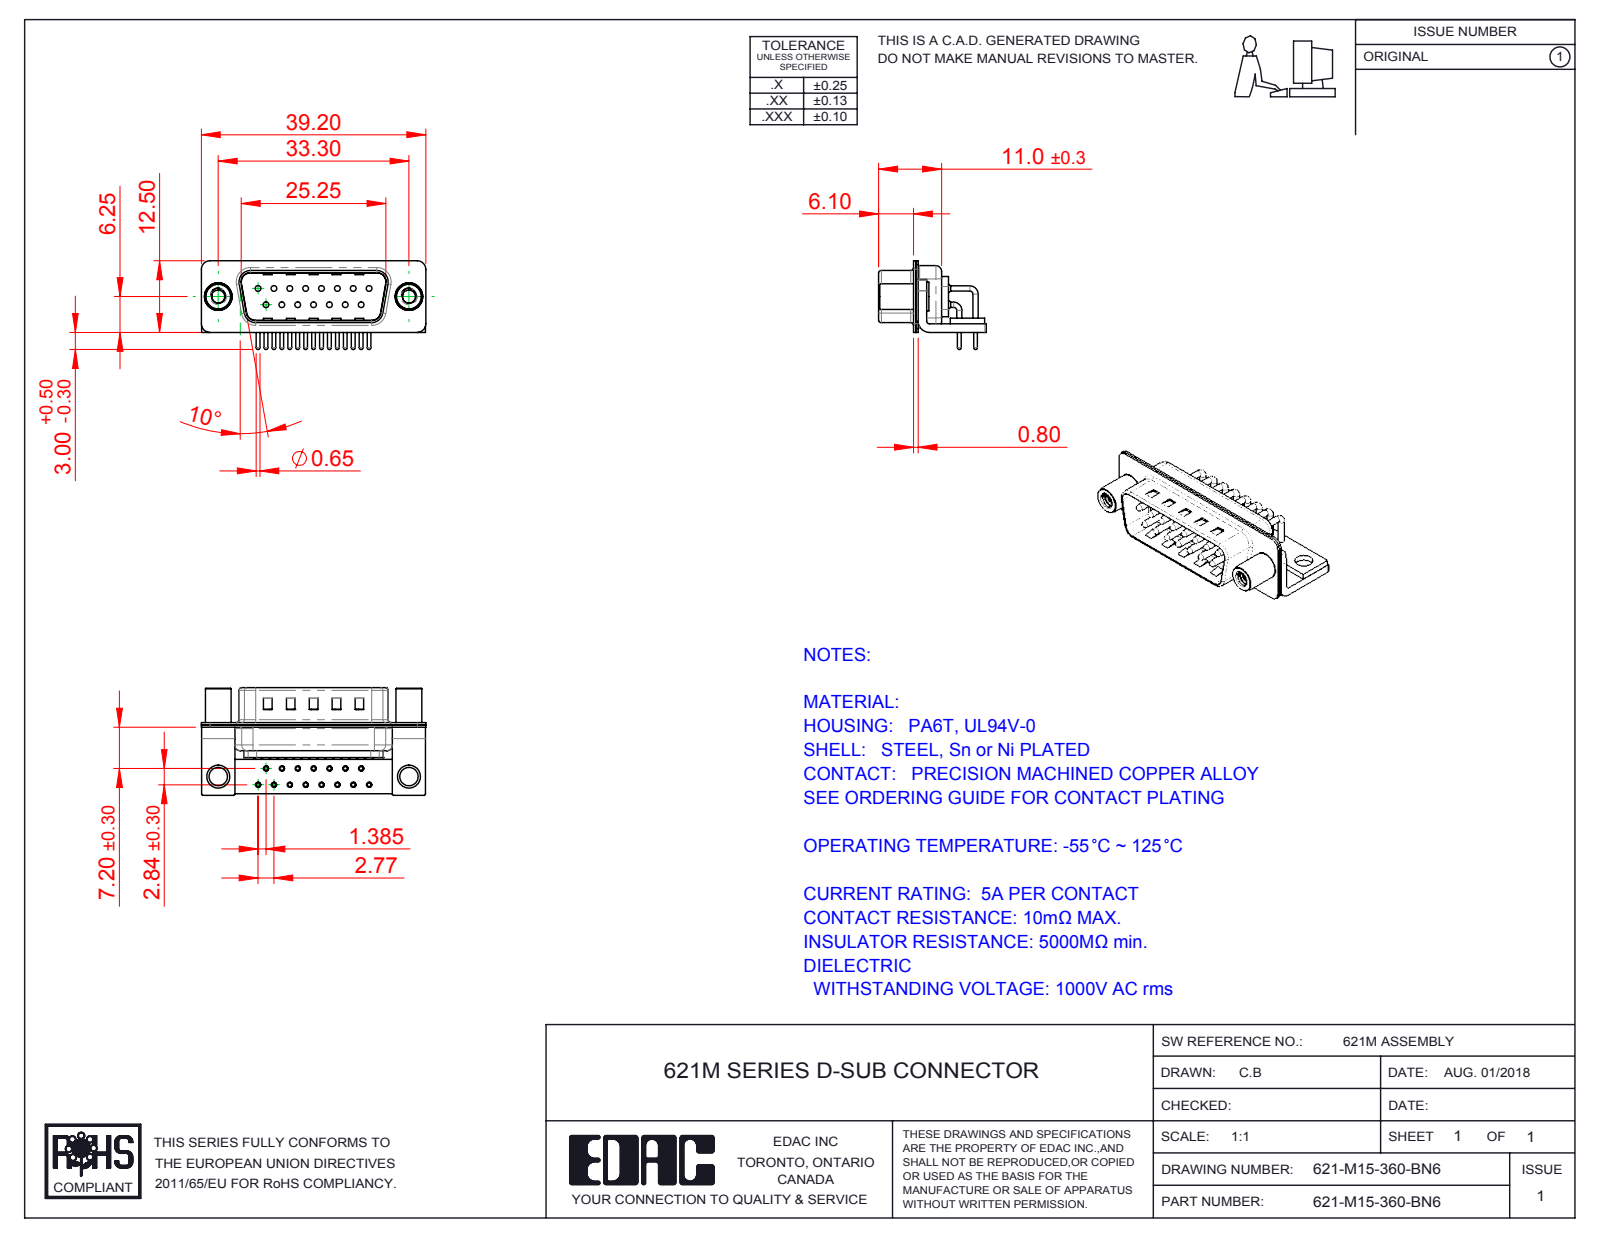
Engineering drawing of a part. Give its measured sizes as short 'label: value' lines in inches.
name: 621-M15-360-BN6; 621M Contact Row 2; 621M Housing_15 Contacts; 621M Shell Front_15 Contacts (+5 more)
written by: SolidWorks 2016 (CONFIG_CONTROL_DESIGN)
unit: in
bodies: 23 solids, 2120 faces (1127 planar, 767 cylindrical, 226 other)
size: 1.543 × 0.74 × 0.61
volume: 0.152 in³; area: 10.34 in²
holes: 15× ⌀0.035, 15× ⌀0.039, 15× ⌀0.067, 15× ⌀0.079, 2× ⌀0.089, 2× ⌀0.126, 2× ⌀0.157, 2× ⌀0.189
bosses: 22× ⌀0.035, 15× ⌀0.059, 15× ⌀0.026, 2× ⌀0.197, 2× ⌀0.193, 2× ⌀0.177
rounds: 16× R0.01, 16× R0.059, 15× R0.04, 13× R0.079, 9× R0.02, 8× R0.063, 4× R0.024, 4× R0.026
face distances: 0.016, 0.033, 0.059, 0.031, 0.049, 0.409, 0.376, 0.075, 0.039, 0.327
hole spacings: 0.124, 0.109, 0.218, 0.327, 0.436, 0.198, 0.198, 0.294
